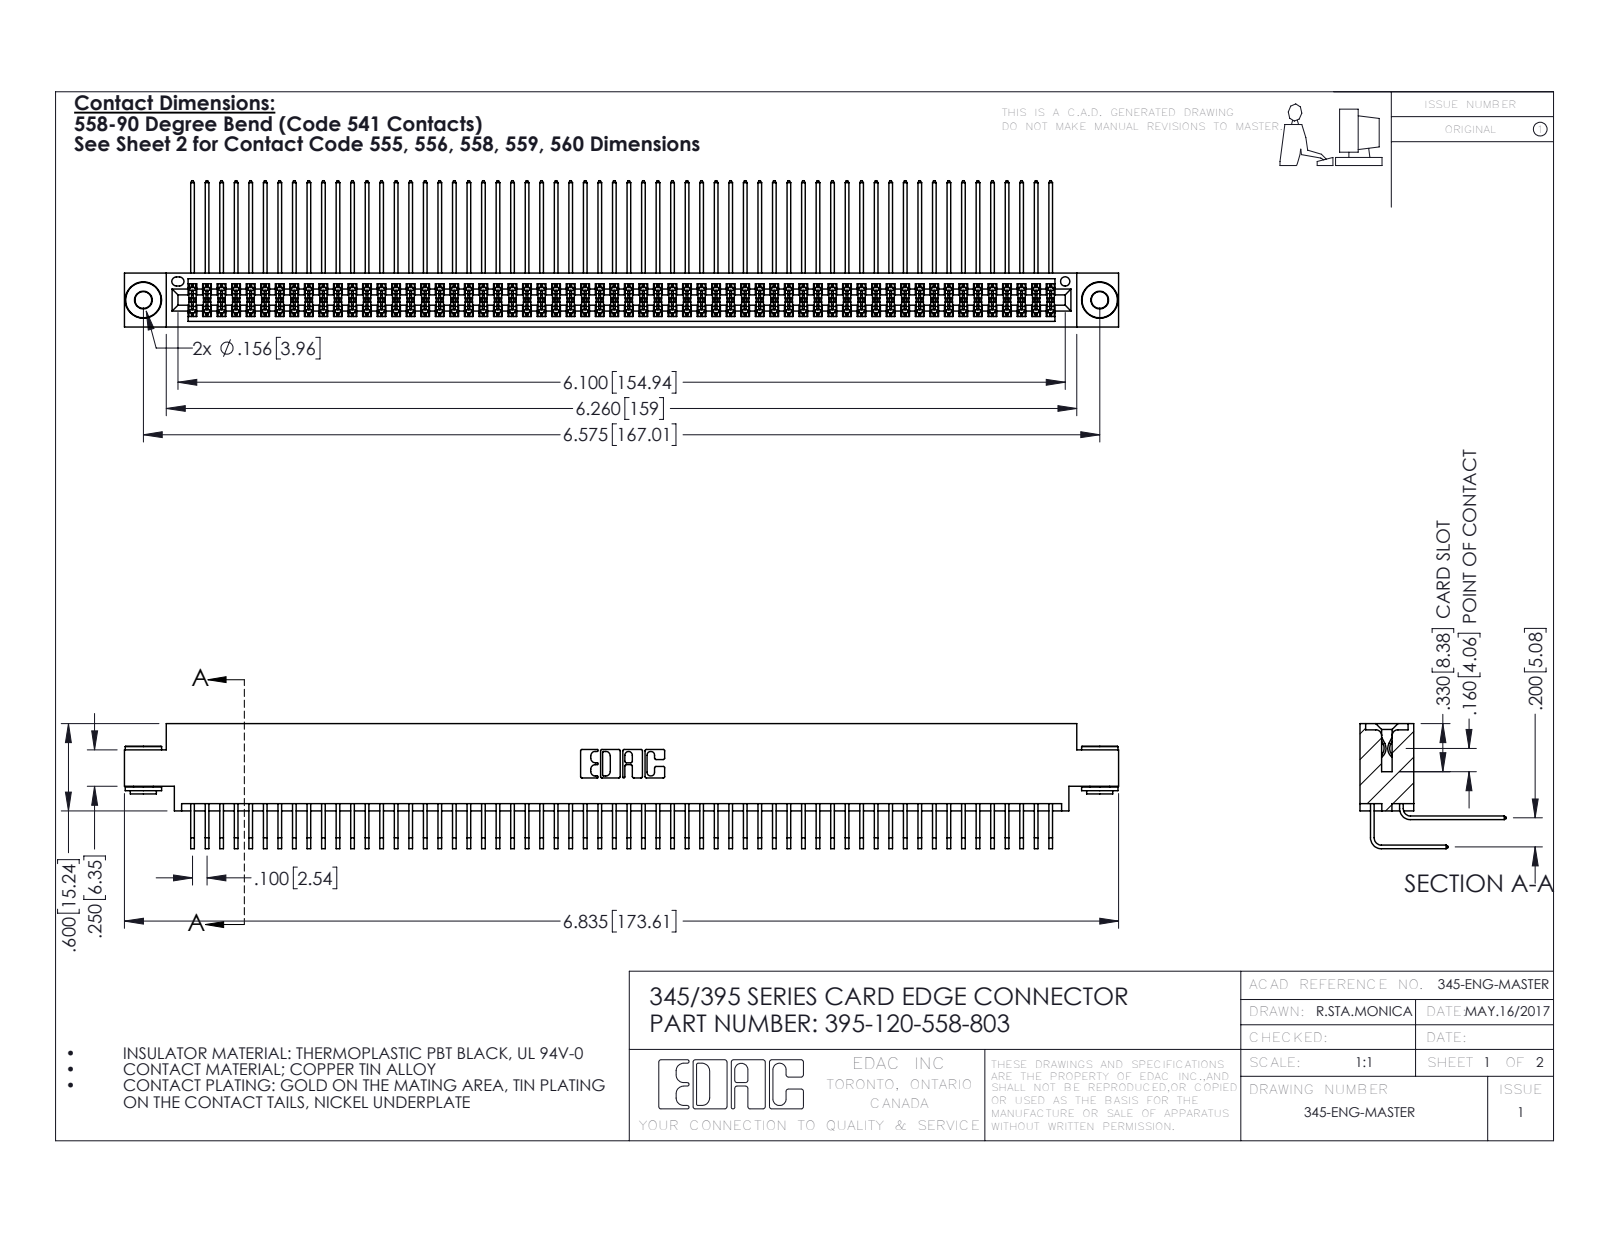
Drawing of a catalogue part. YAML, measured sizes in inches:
part_name: "345-250-002_345-250-002-102; 345-292-001_558 Tail - 2; 345 Part_0.170 Offset - 0.156 Dia-TH; 395-120-558-803 (+1 more)"
step_written_by: "SolidWorks 2016 (CONFIG_CONTROL_DESIGN)"
units: inches
bodies: {solids: 123, faces: 6408, planar: 4294, cylindrical: 2106, other: 8}
overall_size: [6.835, 1.005, 0.859]
volume: 1.076
surface_area: 46.52
round_holes:
  - {diameter: 0.116, count: 2}
  - {diameter: 0.156, count: 2}
  - {diameter: 0.064, count: 1}
round_bosses_or_shafts:
  - {diameter: 0.25, count: 2}
  - {diameter: 0.18, count: 2}
  - {diameter: 0.136, count: 2}
partial_cylinders:
  - {radius: 0.006, count: 181}
  - {radius: 0.01, count: 22}
  - {radius: 0.007, count: 6}
  - {radius: 0.031, count: 6}
  - {radius: 0.026, count: 3}
  - {radius: 0.014, count: 2}
  - {radius: 0.019, count: 2}
  - {radius: 0.022, count: 2}
face_to_face_distances: [0.072, 0.298, 0.2, 0.37, 0.098, 0.272, 0.025, 0.225, 0.175, 0.025]
hole_center_spacings: [0.27, 6.339, 6.575]
